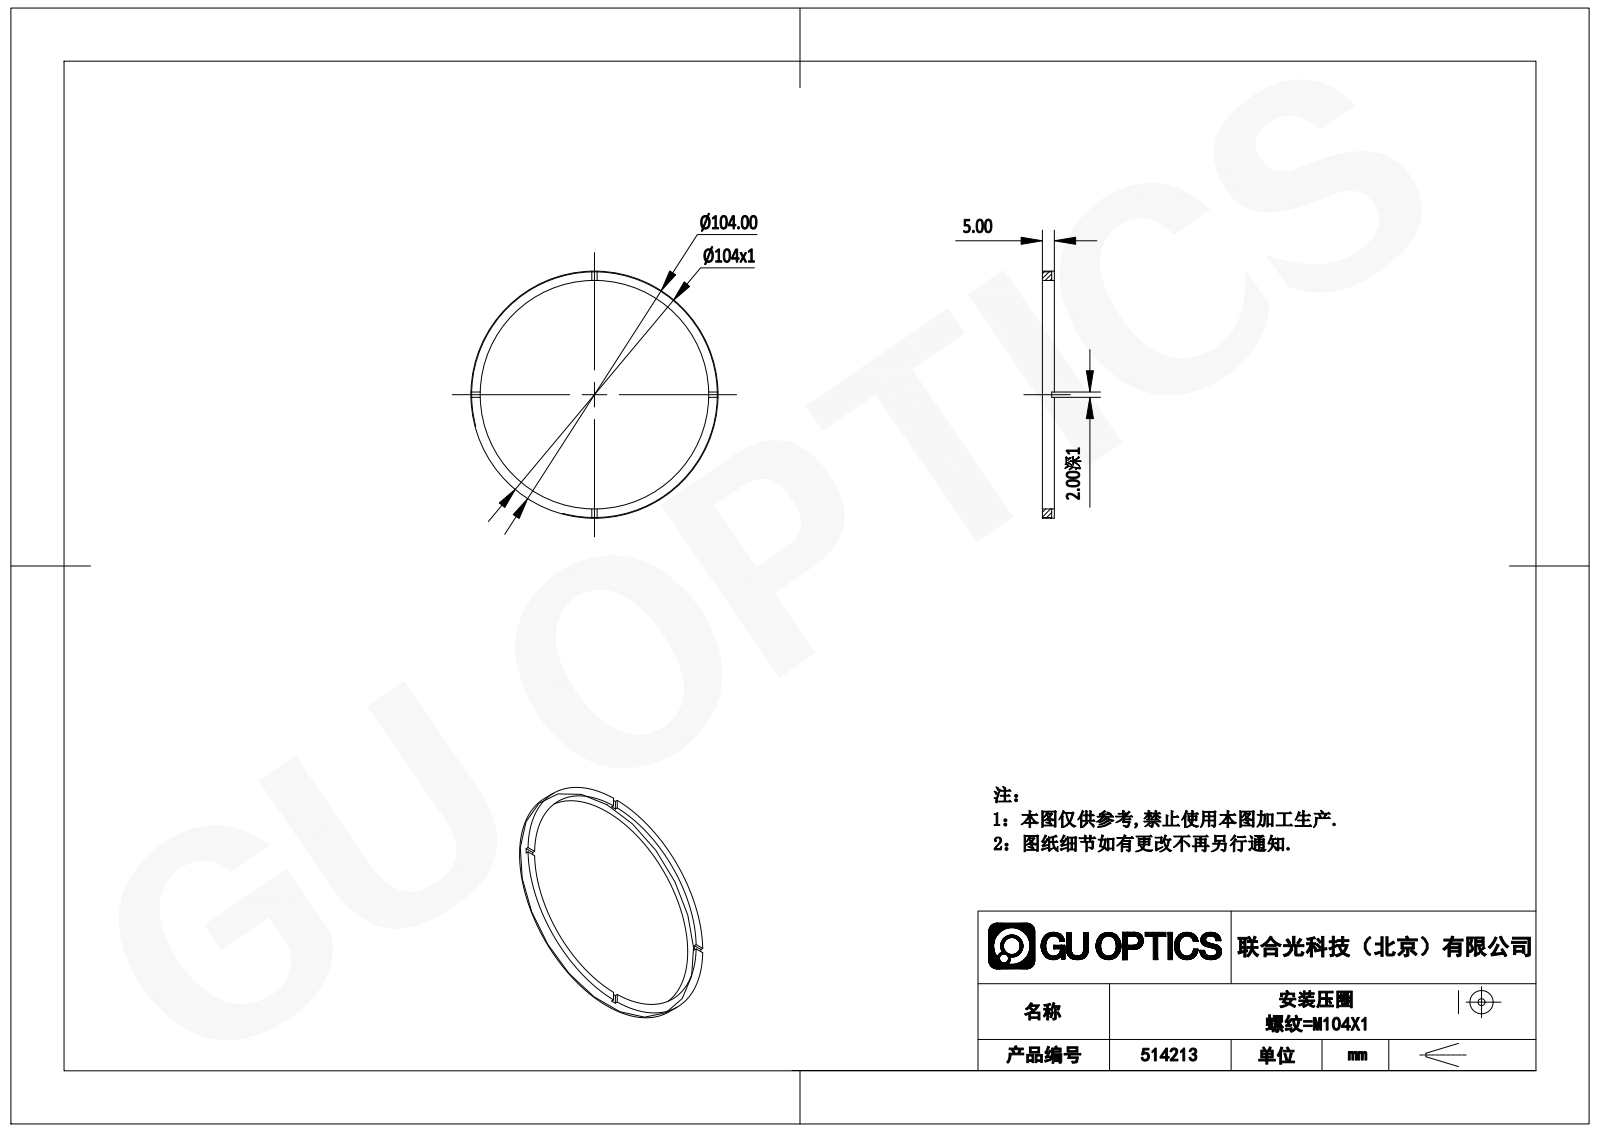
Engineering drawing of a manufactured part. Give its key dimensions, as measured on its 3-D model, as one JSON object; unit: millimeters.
{"part_name": "514213", "step_written_by": "SolidWorks 2020 (CONFIG_CONTROL_DESIGN)", "units": "millimeters", "bodies": {"solids": 1, "faces": 21, "planar": 17, "cylindrical": 4, "other": 0}, "overall_size": [104, 104, 5], "volume_mm3": 6251, "surface_area_mm2": 5671, "round_holes": [[96, 1]], "round_bosses_or_shafts": [[104, 1]], "face_to_face_distances": [5, 4, 1, 2]}
